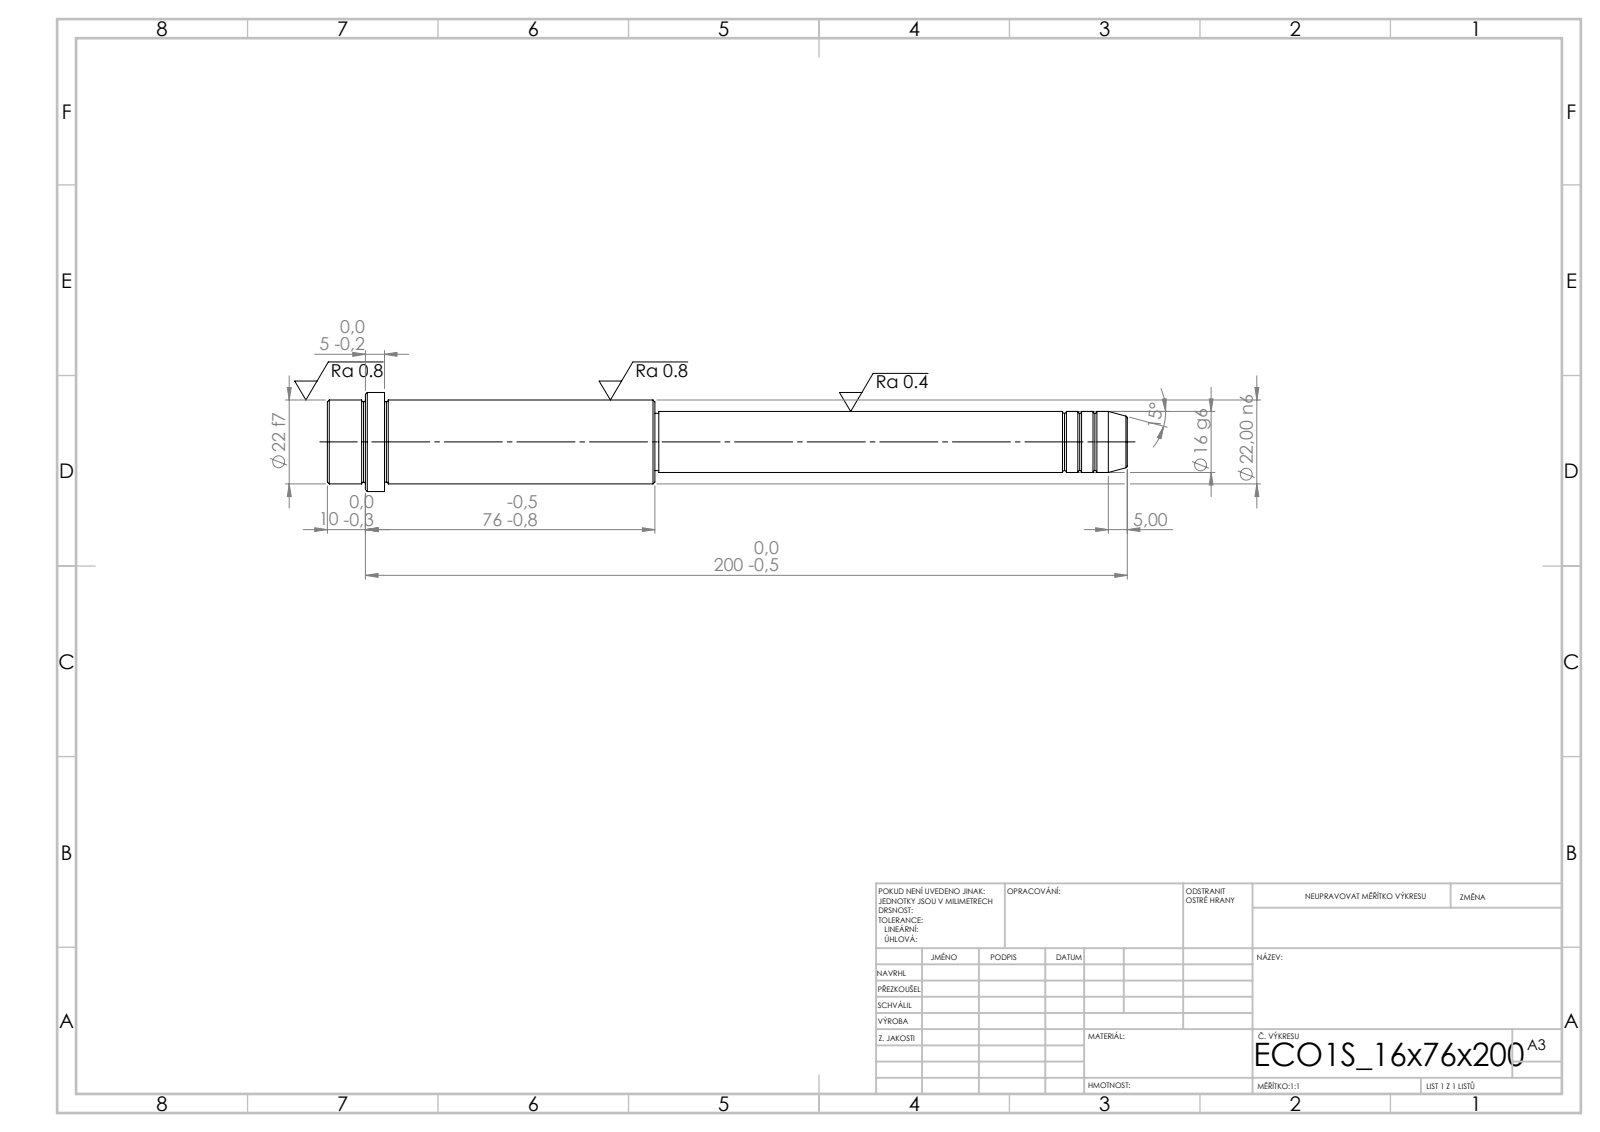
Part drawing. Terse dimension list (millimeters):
written by: SolidWorks 2019 (CONFIG_CONTROL_DESIGN)
unit: mm
bodies: 1 solid, 52 faces (6 planar, 16 cylindrical, 30 other)
size: 210 × 26 × 26
volume: 58 055 mm³; area: 13 352 mm²
bosses: 1× ⌀26, 1× ⌀22, 1× ⌀16, 1× ⌀15
face distances: 86, 71, 15, 124, 195, 210, 200, 76, 5, 10
